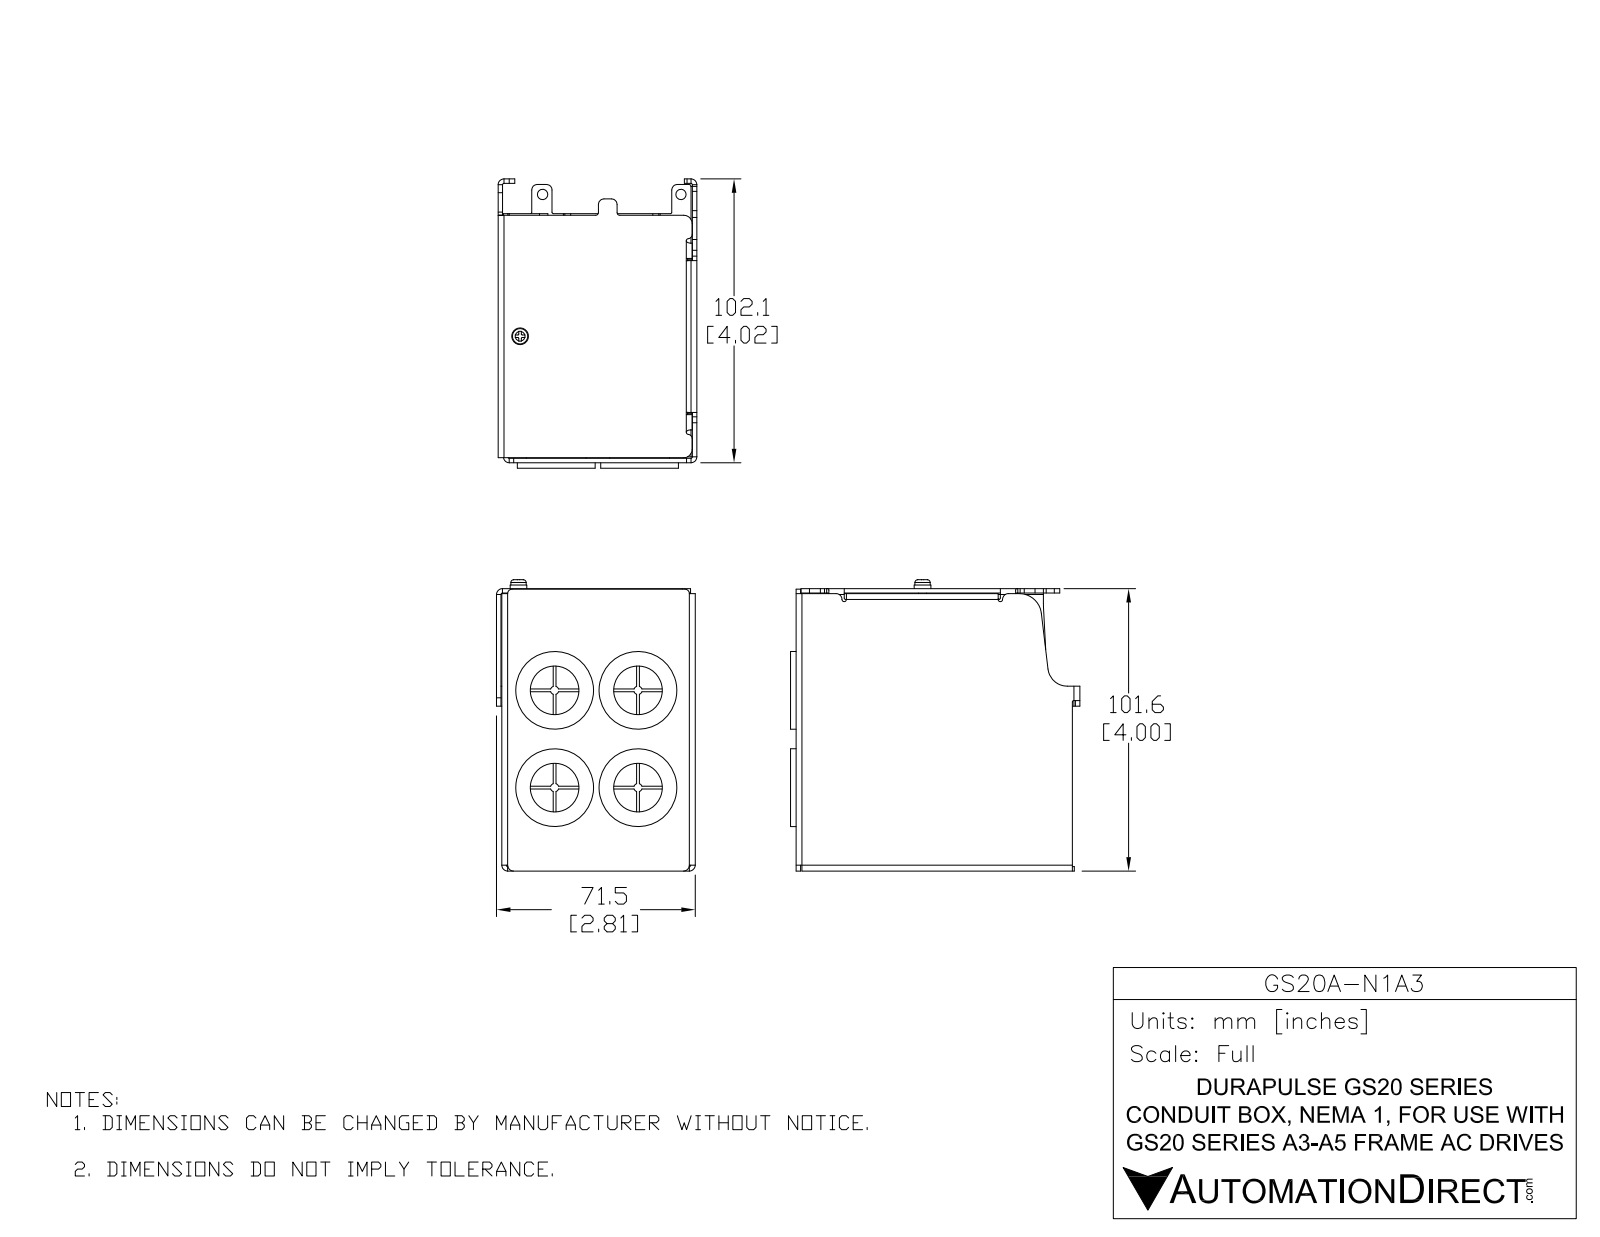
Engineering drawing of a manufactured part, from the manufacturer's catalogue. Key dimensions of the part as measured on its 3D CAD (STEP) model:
Part name (STEP PRODUCT): GS20A-N1A3
STEP written by: SolidWorks 2017 (AUTOMOTIVE_DESIGN)
Units: inches
Bodies: 12 solids, 473 faces (229 planar, 194 cylindrical, 50 other)
Overall size (bounding box): 4.126 × 4.098 × 2.815
Volume: 4.533 in³ · Surface area: 149.9 in²
Round holes (diameter × count): ⌀0.689 ×4, ⌀0.886 ×4, ⌀0.116 ×2, ⌀0.138 ×2, ⌀0.146 ×2, ⌀0.097 ×1, ⌀0.118 ×1, ⌀0.157 ×1
Round bosses / shafts (diameter × count): ⌀1.102 ×4, ⌀0.846 ×4, ⌀0.193 ×3, ⌀0.166 ×3, ⌀0.276 ×2, ⌀0.252 ×2, ⌀0.24 ×2, ⌀0.118 ×2
Partial cylindrical surfaces — rounded edges, fillets, slot ends (radius × count): R0.083 ×22, R0.02 ×21, R0.118 ×9, R0.031 ×7, R0.059 ×7, R0.079 ×7, R0.012 ×4, R0.039 ×4
Main face-to-face distances: 0.063, 2.677, 2.614, 2.74, 0.075, 2.752, 3.937, 3.606, 0.331, 0.138
Hole centre spacings: 0.944, 1.181, 1.378, 1.485, 1.815, 0.669, 1.634, 1.961
